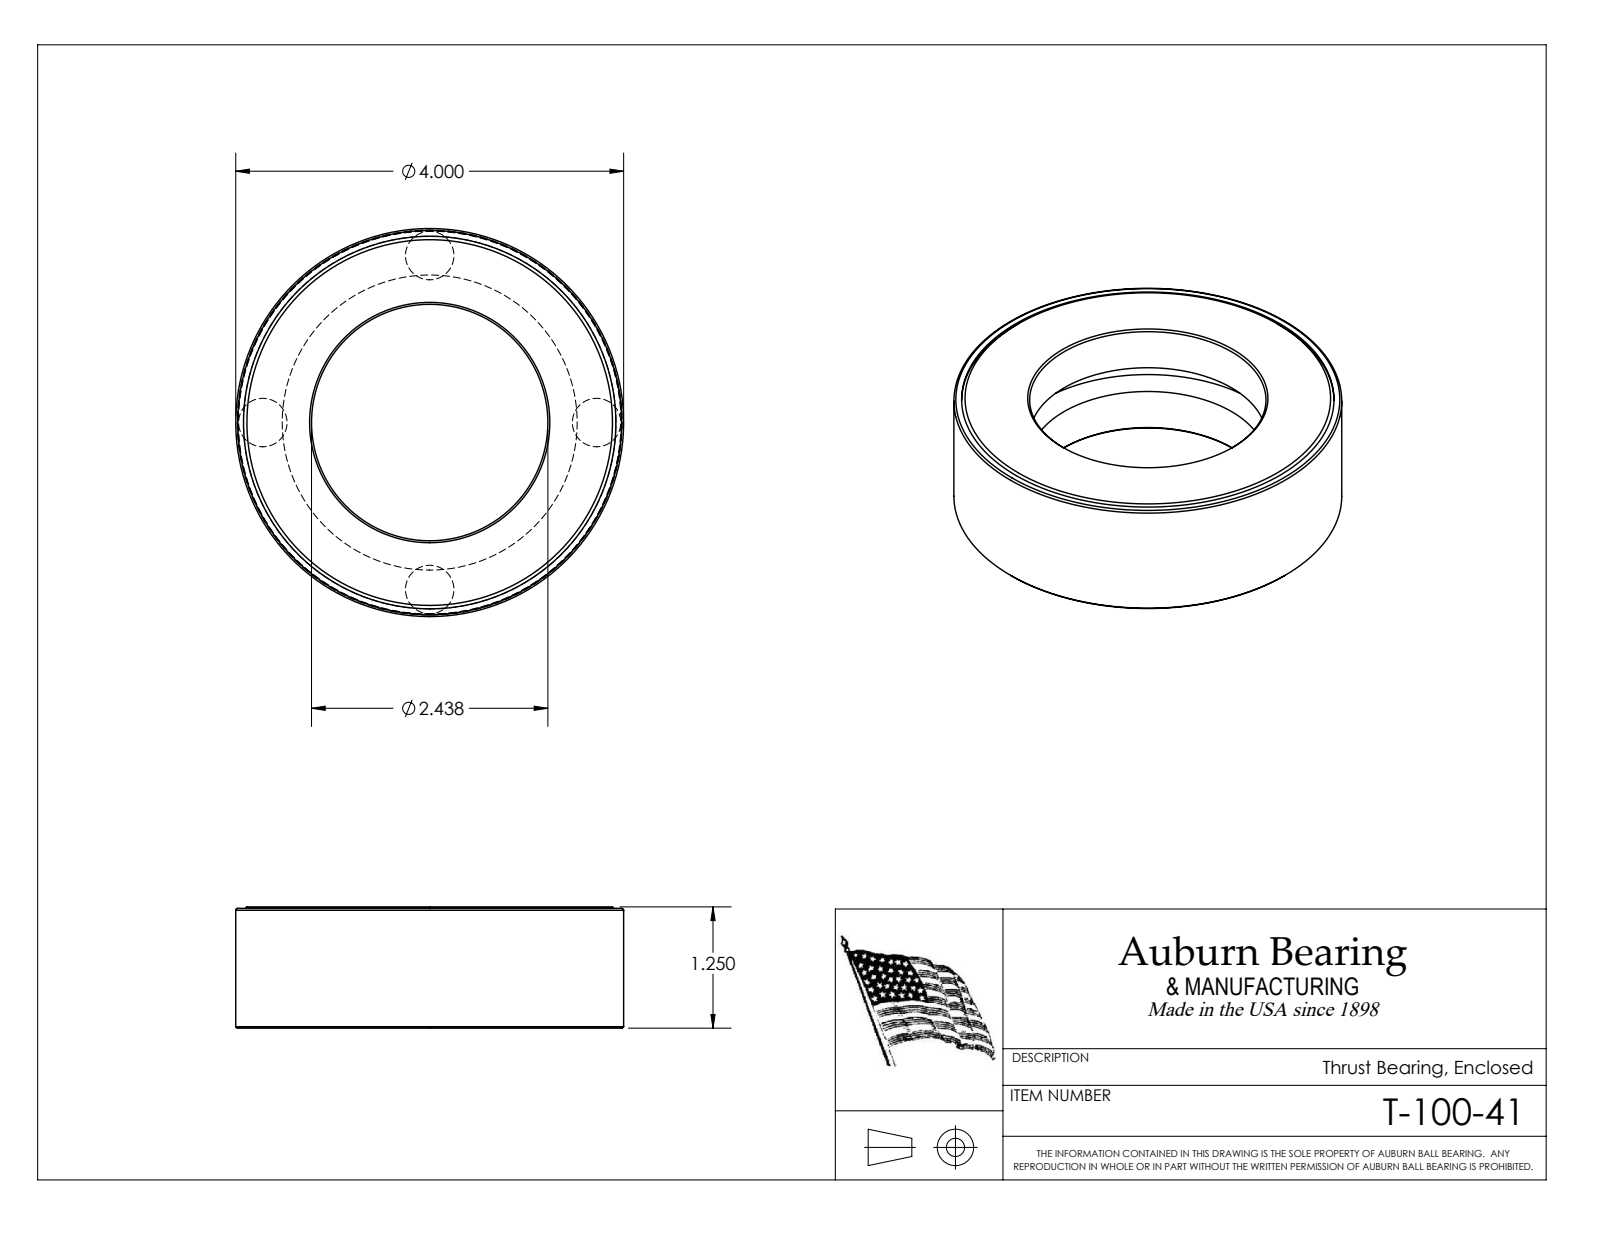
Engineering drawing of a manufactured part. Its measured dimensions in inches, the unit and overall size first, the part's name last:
Units: inches
Overall size (bounding box): 4 × 4 × 1.25
Round holes (diameter × count): ⌀2.437 ×1, ⌀3.84 ×1, ⌀3.96 ×1
Round bosses / shafts (diameter × count): ⌀4 ×1, ⌀3.946 ×1
Main face-to-face distances: 1.25, 0.475, 0.775, 0.775, 0.3, 0.475, 1.215, 1.235, 0.74, 0.76
Volume: 7.154 in³ · Surface area: 74.09 in²
Bodies: 6 solids, 28 faces (9 planar, 7 cylindrical, 12 other)
Part name (STEP PRODUCT): T-100-41
STEP written by: SolidWorks 2016 (CONFIG_CONTROL_DESIGN)
